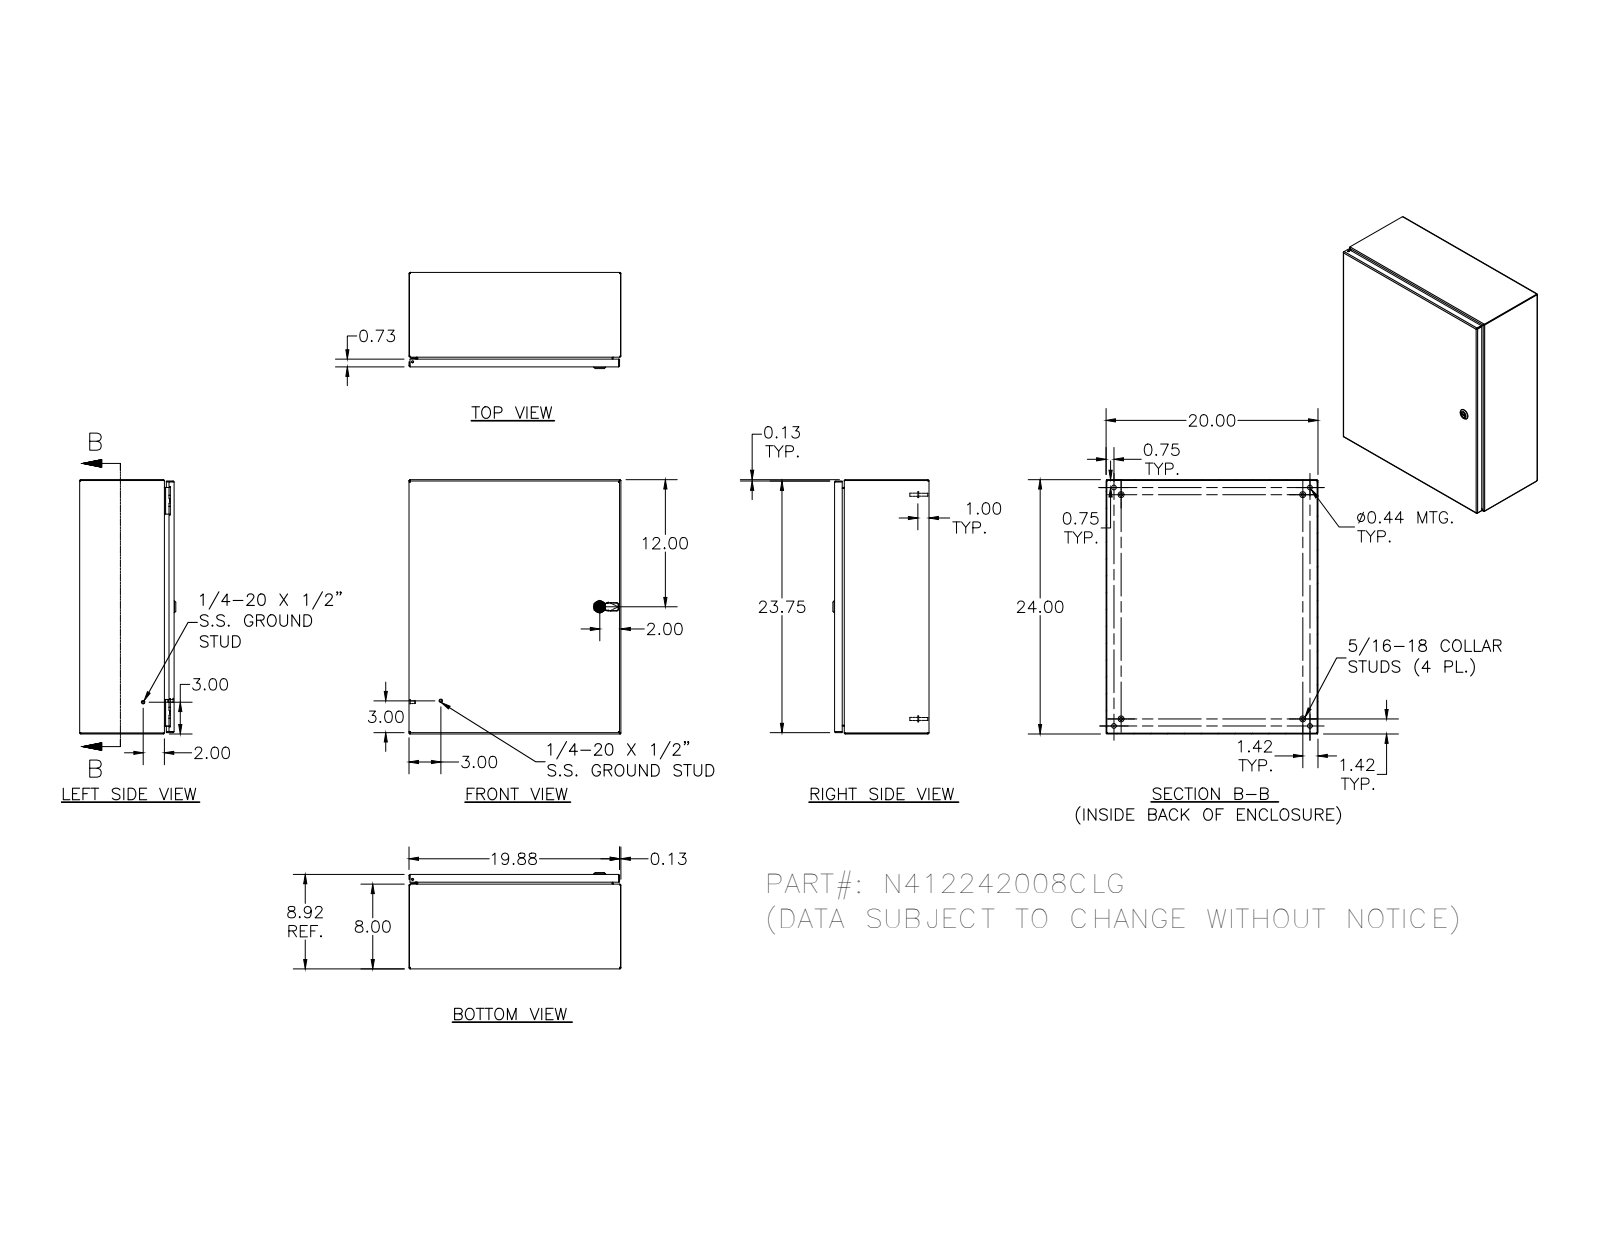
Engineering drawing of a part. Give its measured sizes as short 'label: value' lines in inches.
name: N412242008CLG
written by: SolidWorks 2018 (AUTOMOTIVE_DESIGN)
unit: in
bodies: 33 solids, 1449 faces (530 planar, 547 cylindrical, 372 other)
size: 24 × 20 × 9.075
volume: 136.2 in³; area: 3 702 in²
holes: 5× ⌀0.188, 4× ⌀0.093, 4× ⌀0.152, 4× ⌀0.167, 4× ⌀0.172, 4× ⌀0.437, 2× ⌀0.156, 1× ⌀0.187, 1× ⌀0.197, 1× ⌀0.315, 1× ⌀0.394, 1× ⌀0.402
bosses: 10× ⌀0.25, 4× ⌀0.563, 4× ⌀0.36, 4× ⌀0.32, 4× ⌀0.3, 4× ⌀0.256, 4× ⌀0.164, 4× ⌀0.131
rounds: 30× R0.012, 30× R0.031, 26× R0.05, 20× R0.105, 18× R0.016, 16× R0.125, 13× R0.02, 8× R0.032
face distances: 0.074, 8.843, 8.769, 8.917, 0.074, 19.926, 20, 19.852, 19.926, 23.926
hole spacings: 20, 0.66, 0.656, 1.307, 1.965, 19.34, 20.66, 1.619
